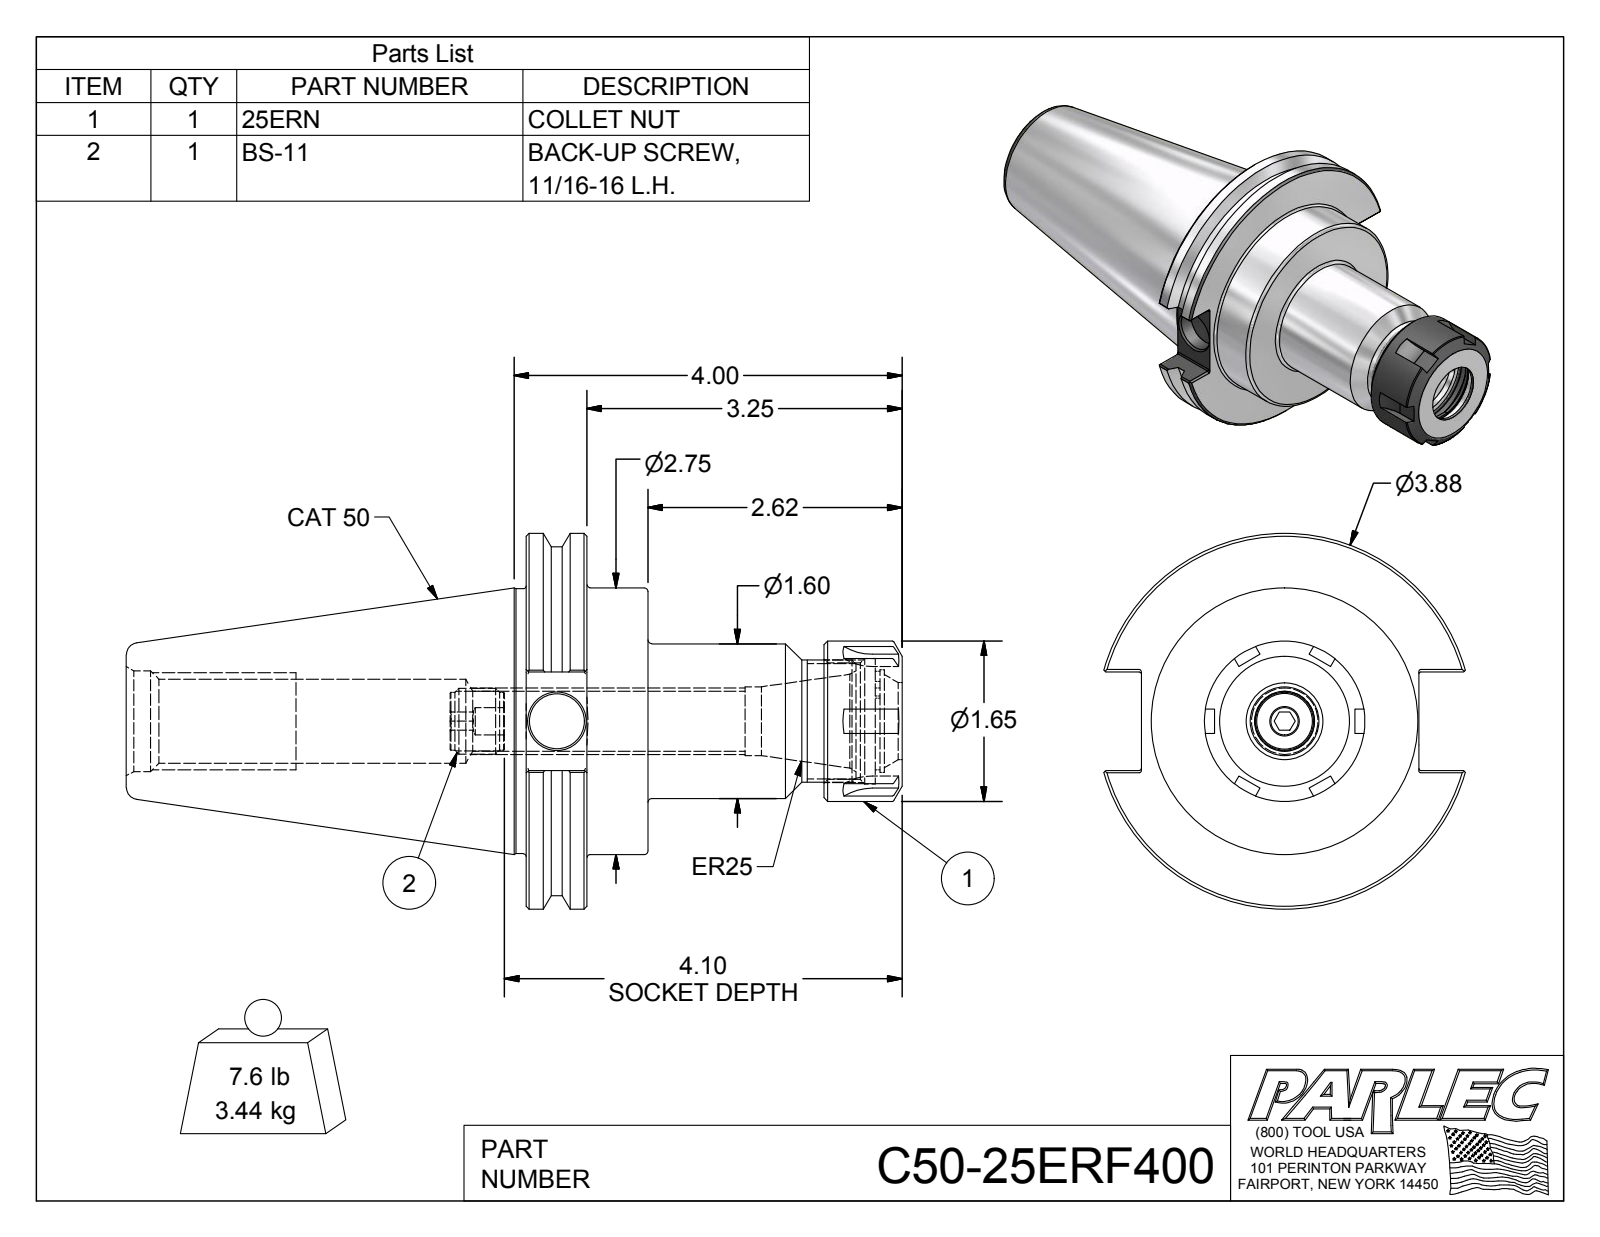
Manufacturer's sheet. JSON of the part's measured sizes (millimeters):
{"part_name": "C50-25ER4-1; 25ERN; BS-11; C50-25ERF400", "step_written_by": "Autodesk Inventor 2016 (AUTOMOTIVE_DESIGN)", "units": "millimeters", "bodies": {"solids": 3, "faces": 195, "planar": 76, "cylindrical": 51, "other": 68}, "overall_size": [203.2, 98.42, 94.71], "volume_mm3": 444655, "surface_area_mm2": 64702, "round_holes": [[7.11, 1], [8, 1], [10.13, 1], [15.75, 1], [18.03, 1], [20.32, 1], [21.97, 1], [26.37, 1], [30.5, 1], [32.88, 1]], "round_bosses_or_shafts": [[98.42, 1], [91.29, 1], [69.85, 1], [69.34, 1], [42, 1], [40.51, 1], [32, 1], [17.3, 1]], "partial_cylinders_radius": [[0.51, 24], [12, 1], [13.06, 1], [13.43, 1]], "face_to_face_distances": [15.88, 31.88, 16, 98.43, 82.55, 66.55, 77.86, 61.98, 45.98, 20.57]}
